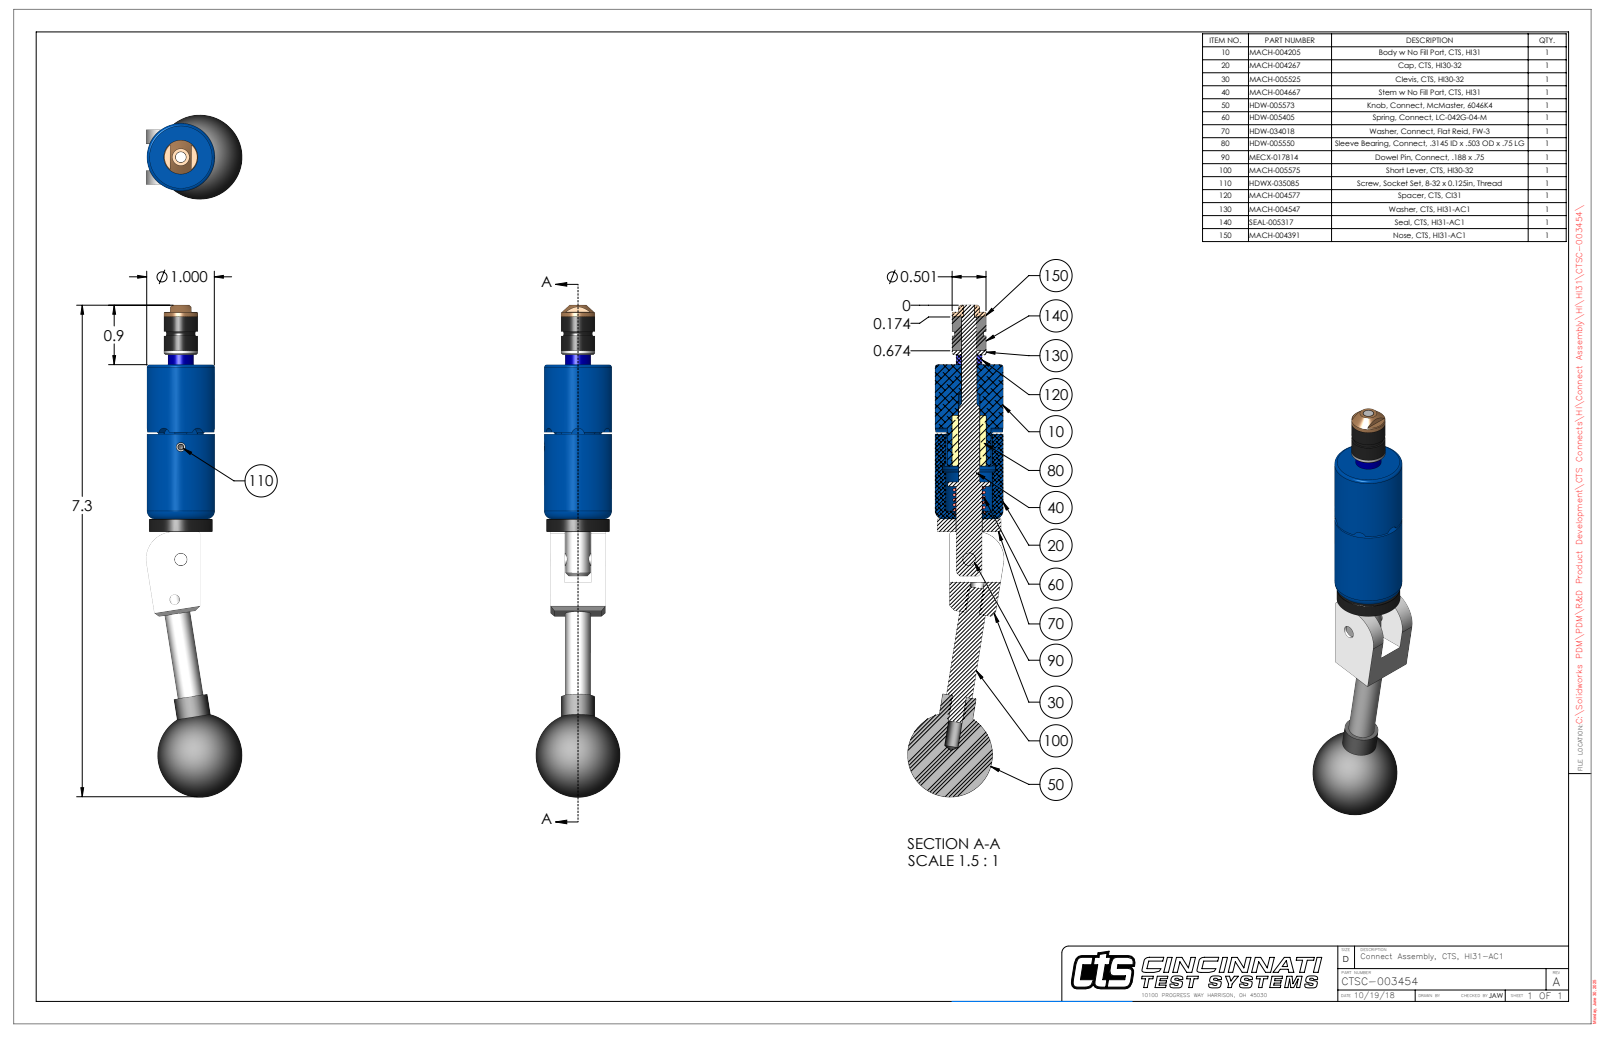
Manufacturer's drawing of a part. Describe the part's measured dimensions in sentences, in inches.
The part is named "CTSC-003454". Its 3-D file was written by "SolidWorks 2023 (AUTOMOTIVE_DESIGN)". It is 10 solids with 253 faces: 98 planar, 98 cylindrical and 57 other. Overall it measures 7.268 by 1.416 by 1.25 inches. Its volume is 3.801 cubic inches and its surface area 31.08 square inches. Round holes: 2 of diameter 0.201, 1 of diameter 0.136, 1 of diameter 0.15, 1 of diameter 0.159, 1 of diameter 0.189, 1 of diameter 0.218, 1 of diameter 0.228, 1 of diameter 0.229, 1 of diameter 0.385, 1 of diameter 0.392. Round bosses or shafts: 1 of diameter 1, 1 of diameter 0.936, 1 of diameter 0.501, 1 of diameter 0.5, 1 of diameter 0.38, 1 of diameter 0.379, 1 of diameter 0.375, 1 of diameter 0.25. Partial cylindrical surfaces (rounded edges, fillets, slot ends): 6 of radius 0.093, 2 of radius 0.029, 1 of radius 0.344, 1 of radius 0.4, 1 of radius 0.478. The main face-to-face distances are 0.21, 0.602, 0.812, 0.187, 2.28, 2.467, 0.391, 1.026, 1.253, 1.441. The hole center spacings are 0.599, 1.658, 2.252.
